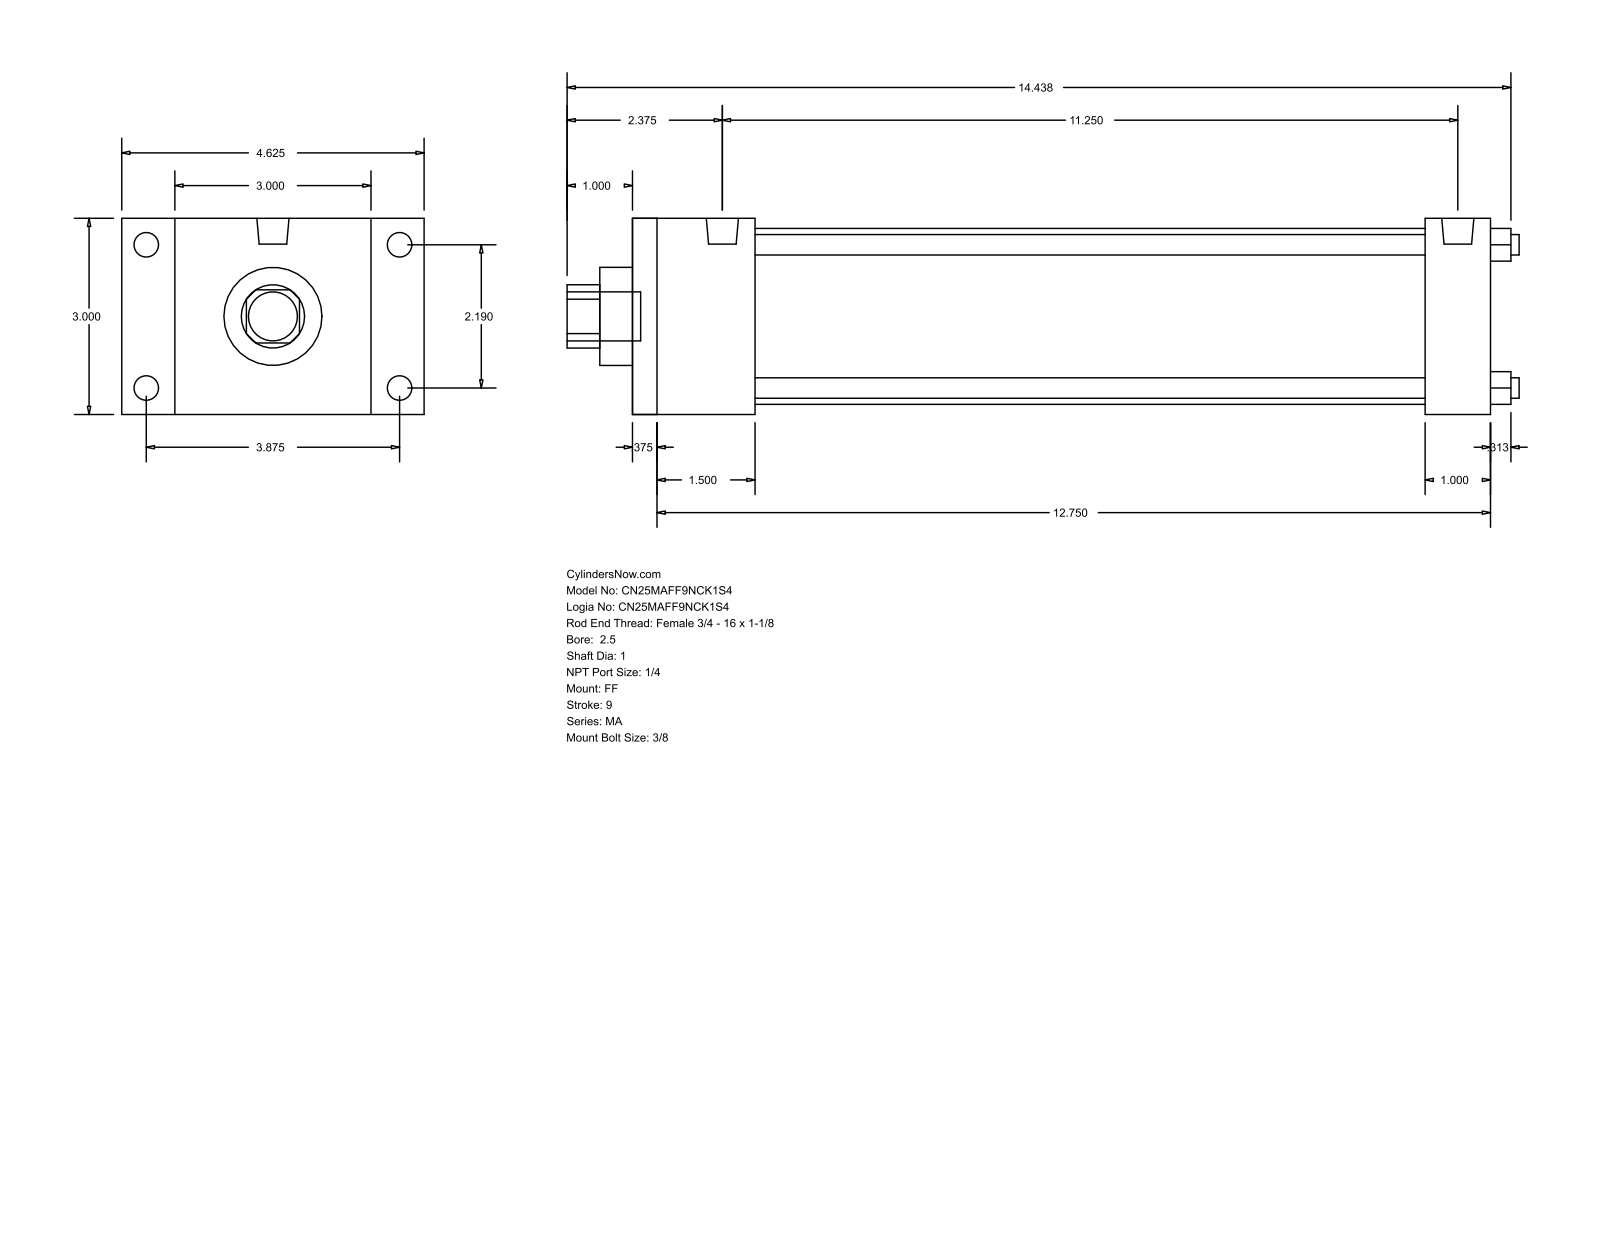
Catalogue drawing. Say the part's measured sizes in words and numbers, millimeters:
The part is named "MA_FF__0250_1". Its 3-D file was written by "GSSL Pune (CONFIG_CONTROL_DESIGN)". It is 0 solids with 92 faces: 64 planar, 28 cylindrical and 0 other. Overall it measures 369.89 by 117.47 by 76.2 millimeters. Round holes: 4 of diameter 7.94, 1 of diameter 25.4, 1 of diameter 38.1, 1 of diameter 68.33. Round bosses or shafts: 4 of diameter 9.53, 4 of diameter 7.94, 2 of diameter 12.49, 1 of diameter 19.05. Partial cylindrical surfaces (rounded edges, fillets, slot ends): 1 of radius 12.29. The main face-to-face distances are 76.2, 333.37, 323.85, 9.52, 25.39, 47.63, 307.98, 38.11, 298.46, 260.35. The hole center spacings are 39.33, 55.62, 78.66.
